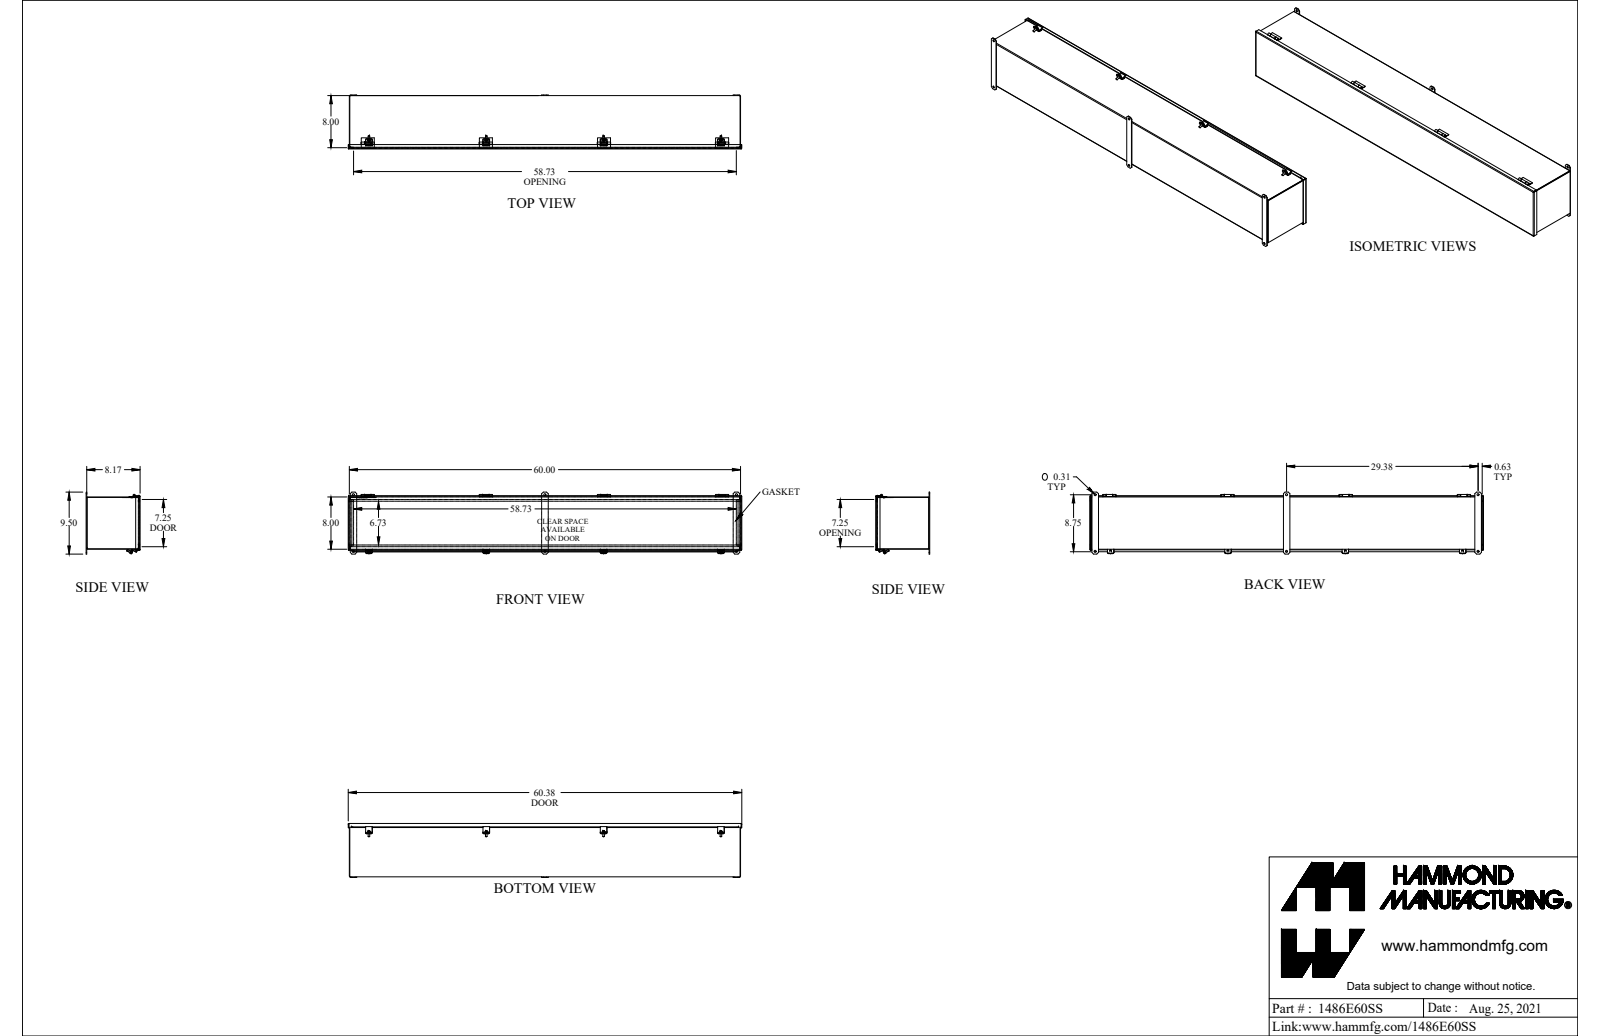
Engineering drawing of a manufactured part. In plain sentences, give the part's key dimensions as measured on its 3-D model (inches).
The part is named "1486E60". Its 3-D file was written by "SolidWorks 2021 (AUTOMOTIVE_DESIGN)". It is 17 solids with 636 faces: 438 planar, 160 cylindrical and 38 other. Overall it measures 60.375 by 9.5 by 8.267 inches. Its volume is 180.6 cubic inches and its surface area 4 692 square inches. Round holes: 6 of diameter 0.313, 4 of diameter 0.213, 1 of diameter 0.187. Round bosses or shafts: 4 of diameter 0.48, 4 of diameter 0.246, 1 of diameter 0.337, 1 of diameter 0.18. Partial cylindrical surfaces (rounded edges, fillets, slot ends): 16 of radius 0.188, 11 of radius 0.036, 11 of radius 0.108, 8 of radius 0.01, 8 of radius 0.03, 8 of radius 0.141, 2 of radius 0.029, 2 of radius 0.086. The main face-to-face distances are 0.072, 7.928, 8.1, 7.856, 8, 8.028, 8.172, 0.187, 0.259, 59.928. The hole center spacings are 8.688, 18, 29.375, 30.633, 36, 29.375, 30.633, 54.
